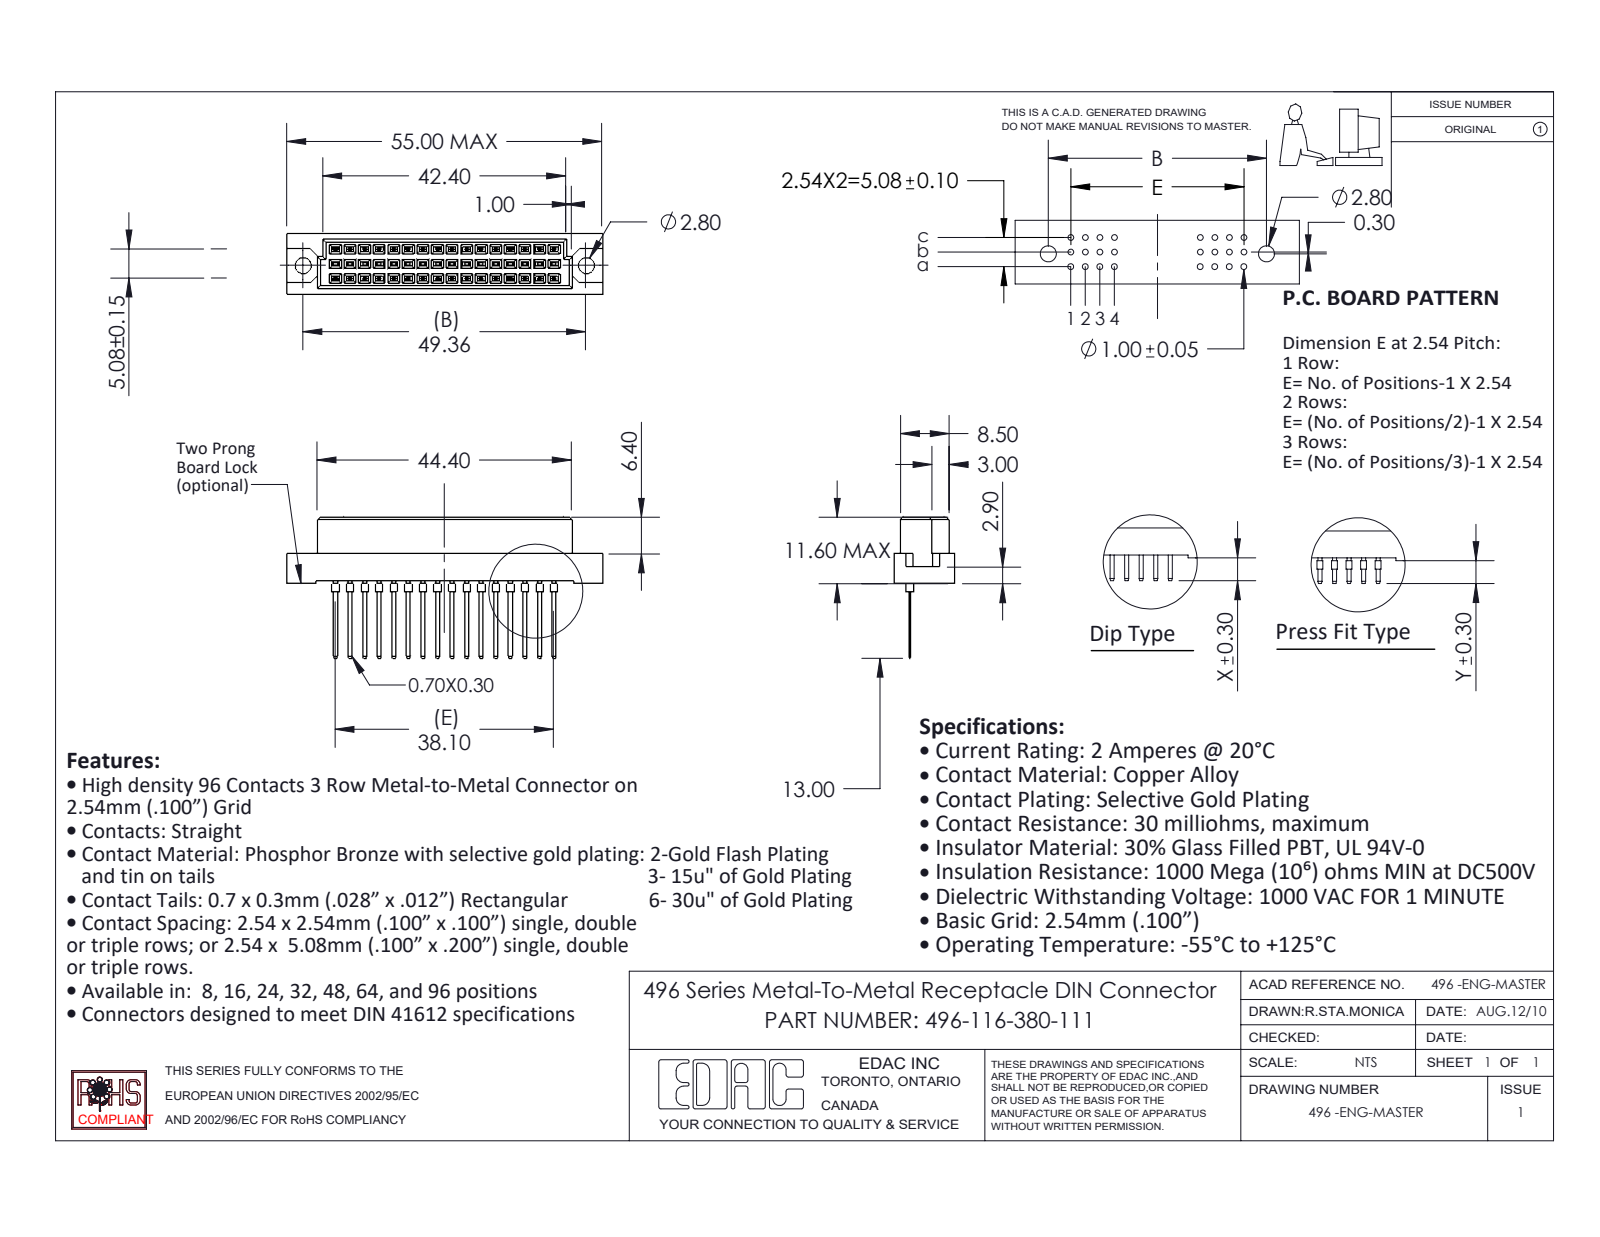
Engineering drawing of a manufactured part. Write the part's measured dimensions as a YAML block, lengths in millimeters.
part_name: "496-290_80; 496 Part_48; 496-116-380-111"
step_written_by: "SolidWorks 2020 (CONFIG_CONTROL_DESIGN)"
units: millimeters
bodies: {solids: 17, faces: 954, planar: 918, cylindrical: 36, other: 0}
overall_size: [55, 24.6, 10.6]
volume: 4662
surface_area: 4821
round_holes:
  - {diameter: 2.8, count: 2}
round_bosses_or_shafts:
  - {diameter: 1, count: 16}
face_to_face_distances: [2.54, 5.08, 1.05, 9.55, 0.81, 2.61, 2.91, 7.69, 7.99, 1.56]
hole_center_spacings: [49.36]
